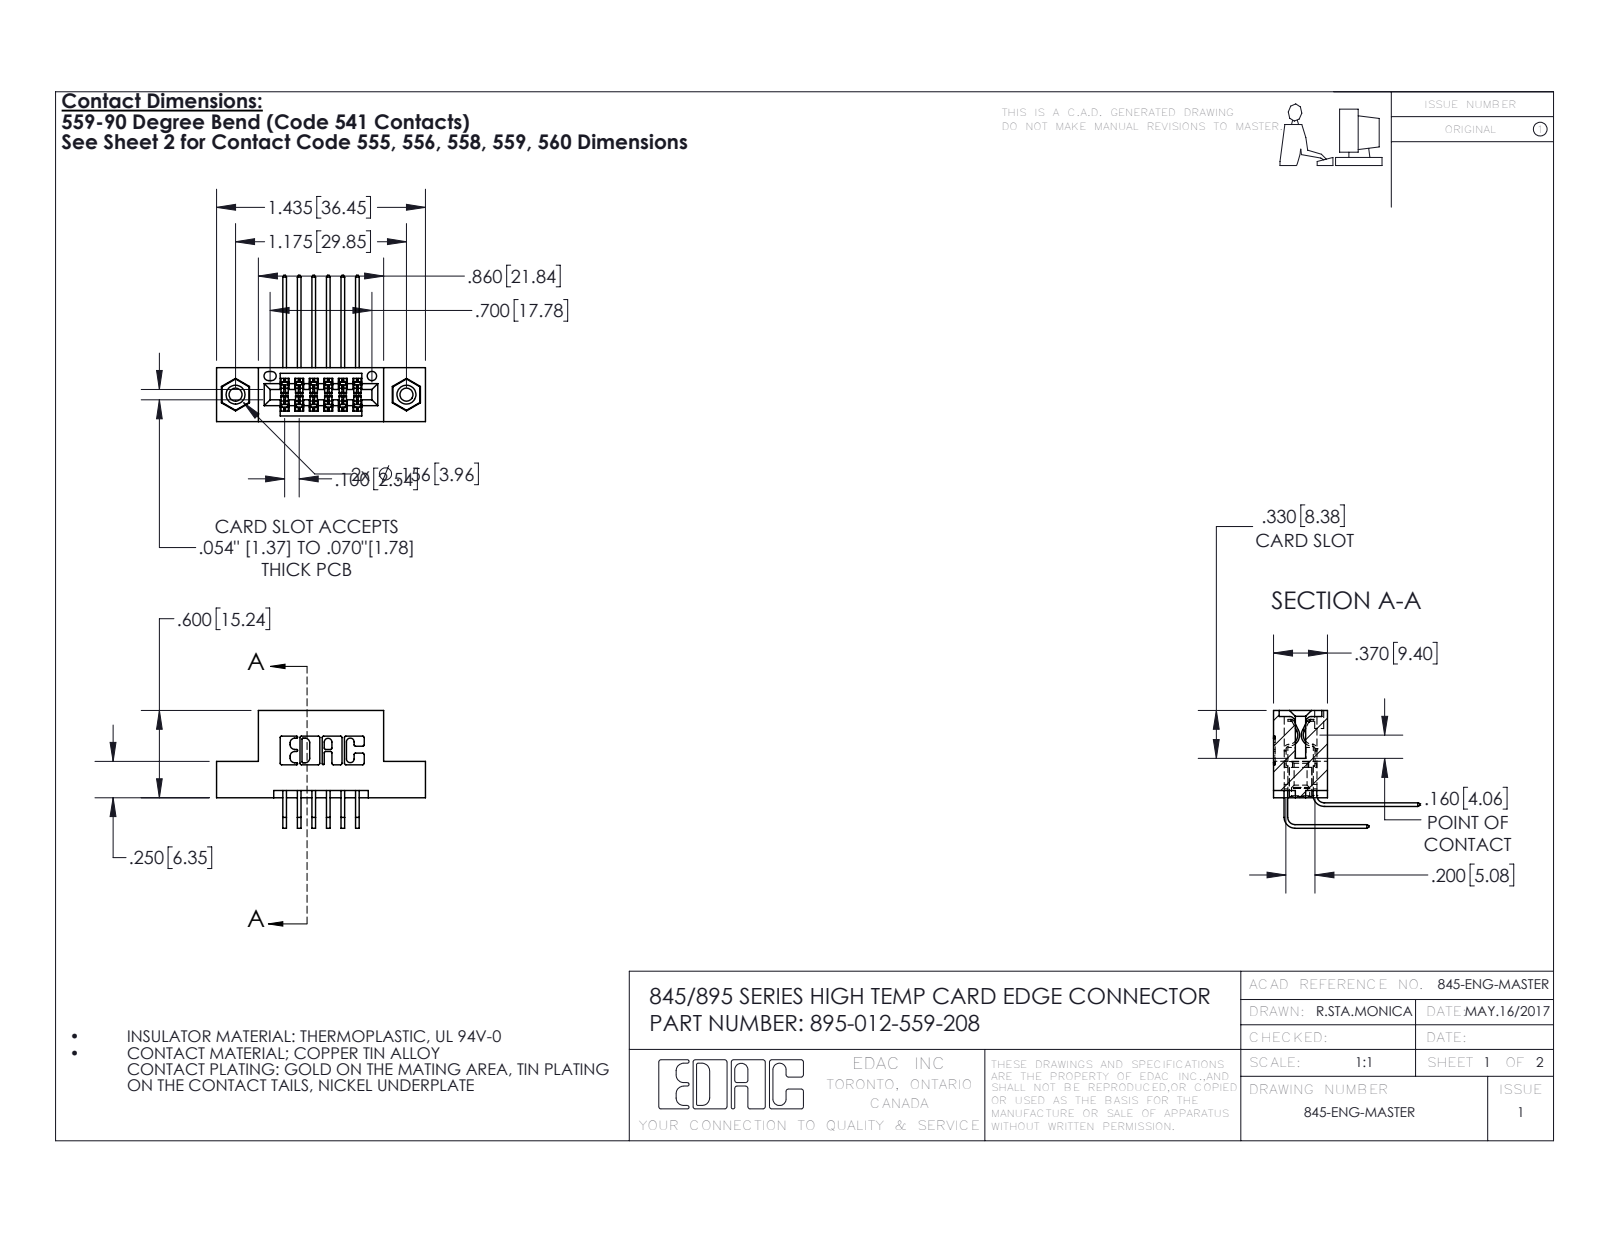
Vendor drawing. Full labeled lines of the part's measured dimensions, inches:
Part name (STEP PRODUCT): 345-250-001_345-250-003-102; 345-292-001_559 Tail - 2; 345-292-001_558 559 Tail - 1; 345 Part_Flush Mounting Lugs - 0.156 Dia-TI (+1 more)
STEP written by: SolidWorks 2016 (CONFIG_CONTROL_DESIGN)
Units: inches
Bodies: 15 solids, 810 faces (532 planar, 262 cylindrical, 16 other)
Overall size (bounding box): 1.435 × 1.005 × 0.809
Volume: 0.2 in³ · Surface area: 6.935 in²
Round holes (diameter × count): ⌀0.089 ×2, ⌀0.125 ×2, ⌀0.156 ×2, ⌀0.064 ×1
Round bosses / shafts (diameter × count): ⌀0.155 ×2
Partial cylindrical surfaces — rounded edges, fillets, slot ends (radius × count): R0.01 ×22, R0.006 ×18, R0.007 ×6, R0.031 ×6, R0.026 ×3, R0.014 ×2, R0.019 ×2, R0.022 ×2
Main face-to-face distances: 0.2, 0.1, 0.072, 0.298, 0.37, 0.098, 0.272, 0.025, 0.15, 0.3
Hole centre spacings: 0.27, 0.946, 1.175
